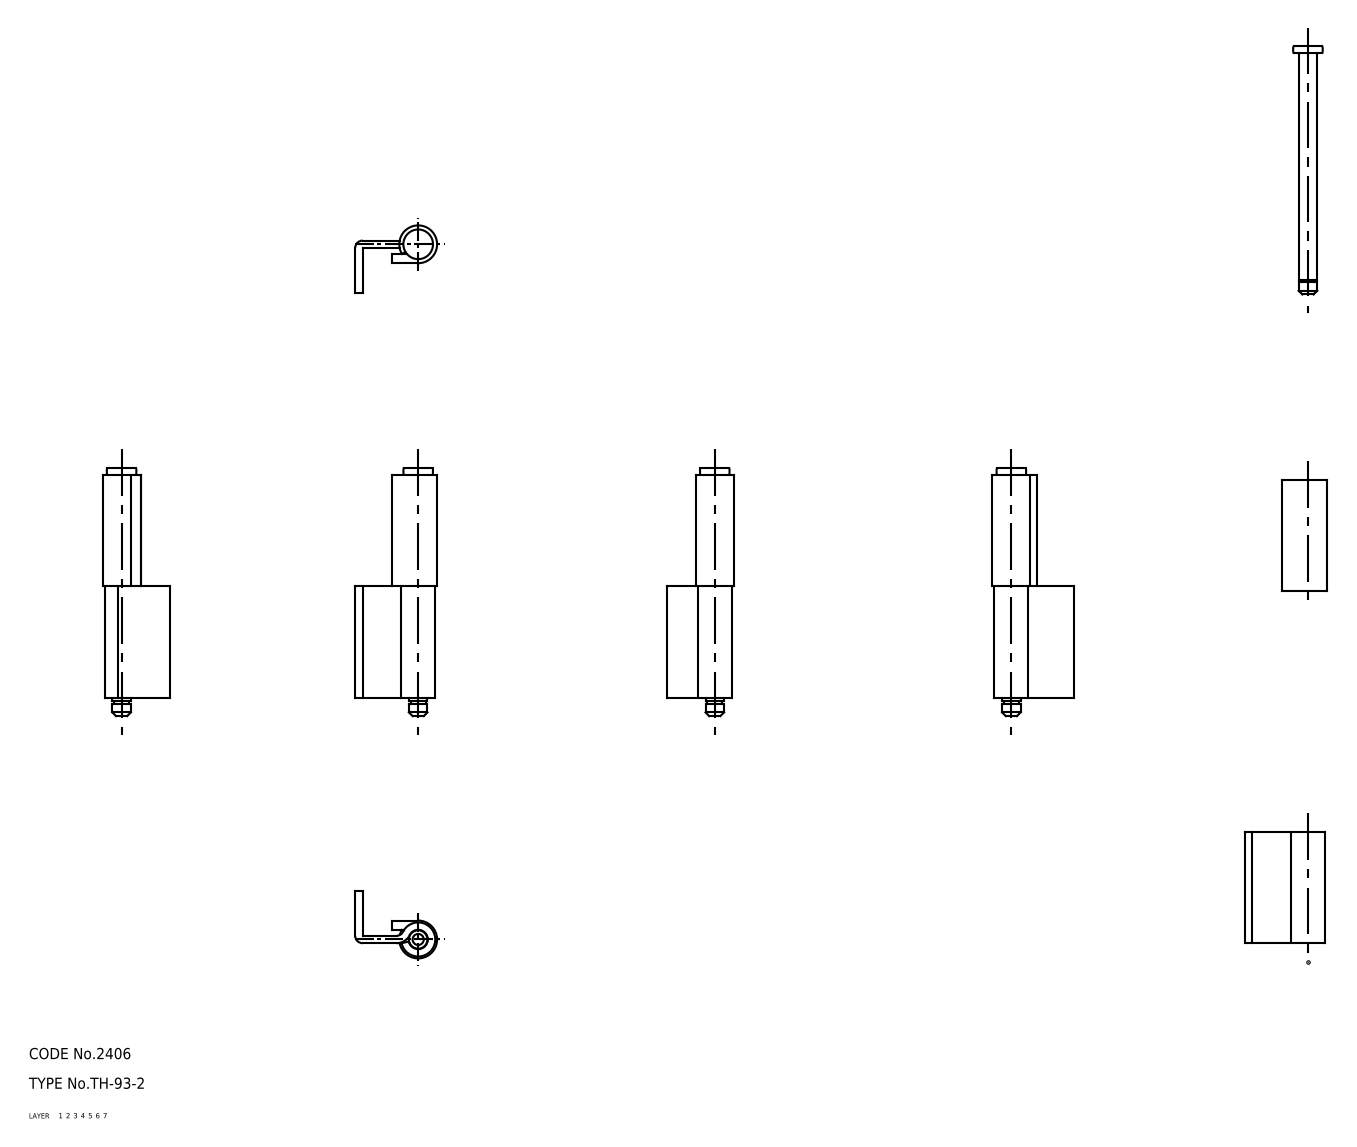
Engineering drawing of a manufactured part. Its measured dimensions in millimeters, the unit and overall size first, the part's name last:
Units: millimetres
Overall size (bounding box): 67 × 22.1 × 18.1
Volume: 6 170 mm³ · Surface area: 6 156 mm²
Bodies: 3 solids, 35 faces (0 planar, 0 cylindrical, 35 other)
Part name (STEP PRODUCT): shaft; hinge piece_B; hinge piece_A; TH_93_2_18800_36
STEP written by: CADfix (AUTOMOTIVE_DESIGN)
